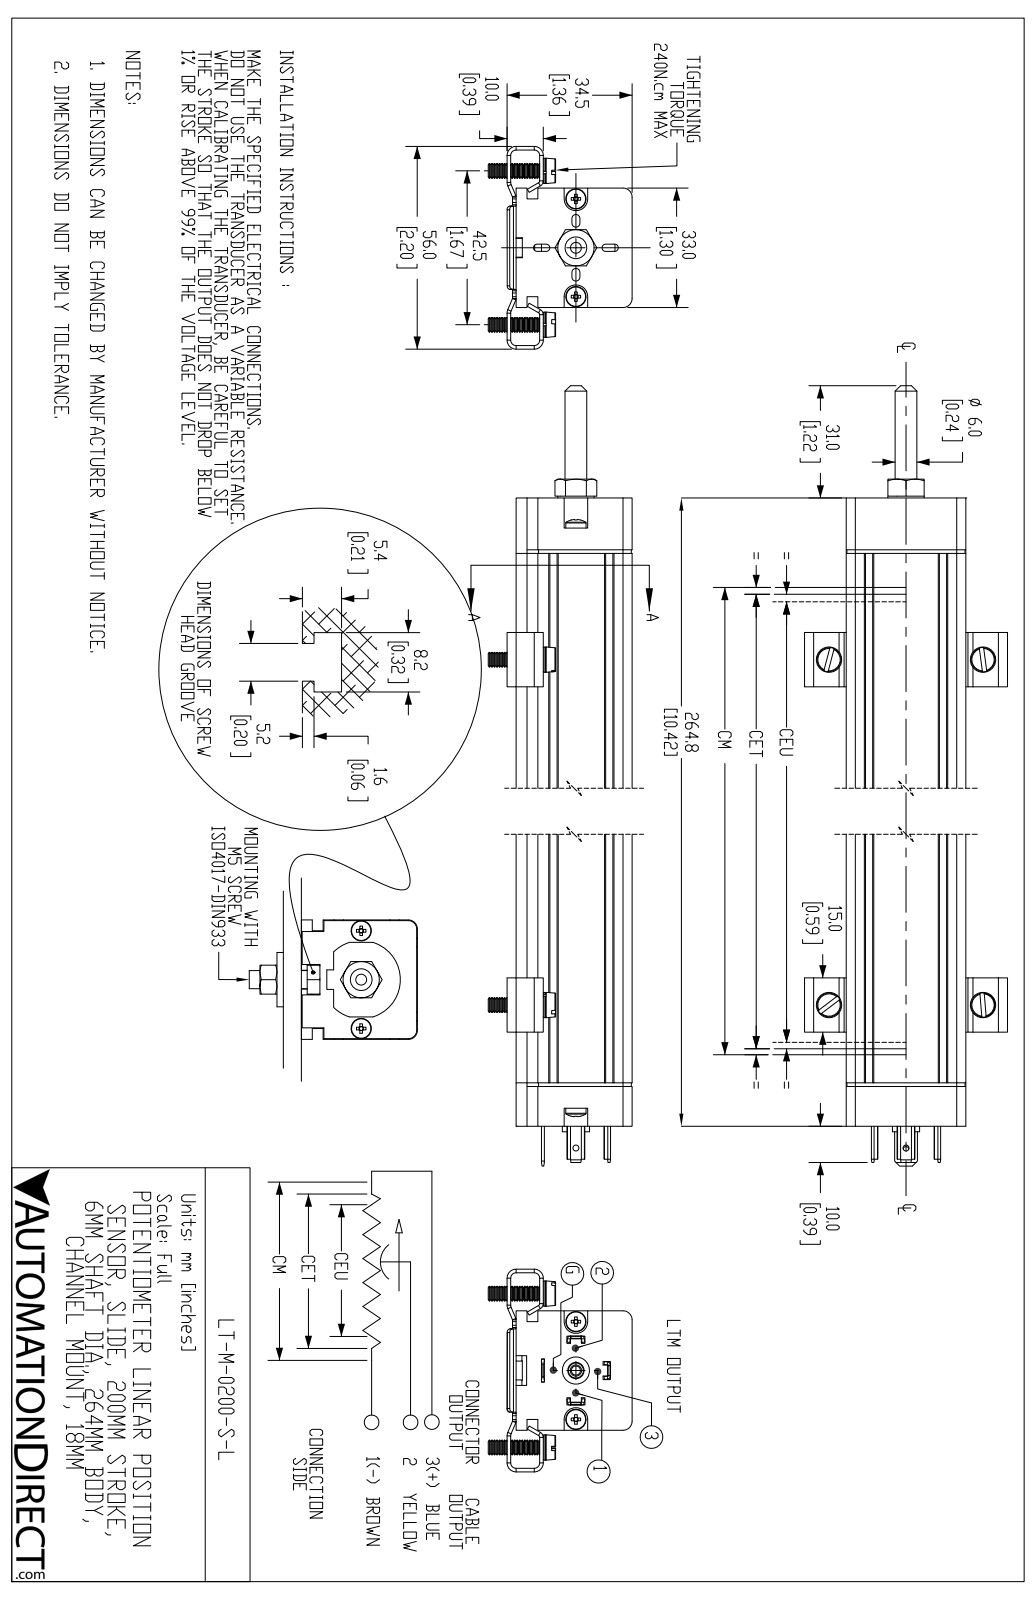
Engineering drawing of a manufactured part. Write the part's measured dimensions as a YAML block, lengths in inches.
part_name: "LT-M-0200-S-L"
step_written_by: "SolidWorks 2019 (AUTOMOTIVE_DESIGN)"
units: inches
bodies: {solids: 21, faces: 1620, planar: 696, cylindrical: 356, other: 568}
overall_size: [12.773, 2.205, 1.563]
volume: 16.48
surface_area: 103.8
round_holes:
  - {diameter: 0.142, count: 4}
  - {diameter: 0.059, count: 2}
  - {diameter: 0.065, count: 2}
  - {diameter: 0.108, count: 2}
  - {diameter: 0.134, count: 2}
  - {diameter: 0.169, count: 2}
  - {diameter: 0.063, count: 1}
  - {diameter: 0.098, count: 1}
  - {diameter: 0.118, count: 1}
  - {diameter: 0.163, count: 1}
  - {diameter: 0.197, count: 1}
  - {diameter: 0.276, count: 1}
round_bosses_or_shafts:
  - {diameter: 0.274, count: 4}
  - {diameter: 0.157, count: 4}
  - {diameter: 0.22, count: 2}
  - {diameter: 0.118, count: 2}
  - {diameter: 0.295, count: 1}
  - {diameter: 0.236, count: 1}
  - {diameter: 0.177, count: 1}
  - {diameter: 0.173, count: 1}
partial_cylinders:
  - {radius: 0.039, count: 34}
  - {radius: 0.098, count: 12}
  - {radius: 0.059, count: 10}
  - {radius: 0.085, count: 8}
  - {radius: 0.033, count: 6}
  - {radius: 0.043, count: 4}
  - {radius: 0.024, count: 2}
  - {radius: 0.063, count: 2}
face_to_face_distances: [1.299, 1.26, 0.118, 0.039, 1.287, 0.213, 0.059, 0.488, 1.047, 0.799]
hole_center_spacings: [0.484, 0.531, 1.359, 1.663, 1.673, 1.766, 1.78, 7.787]
